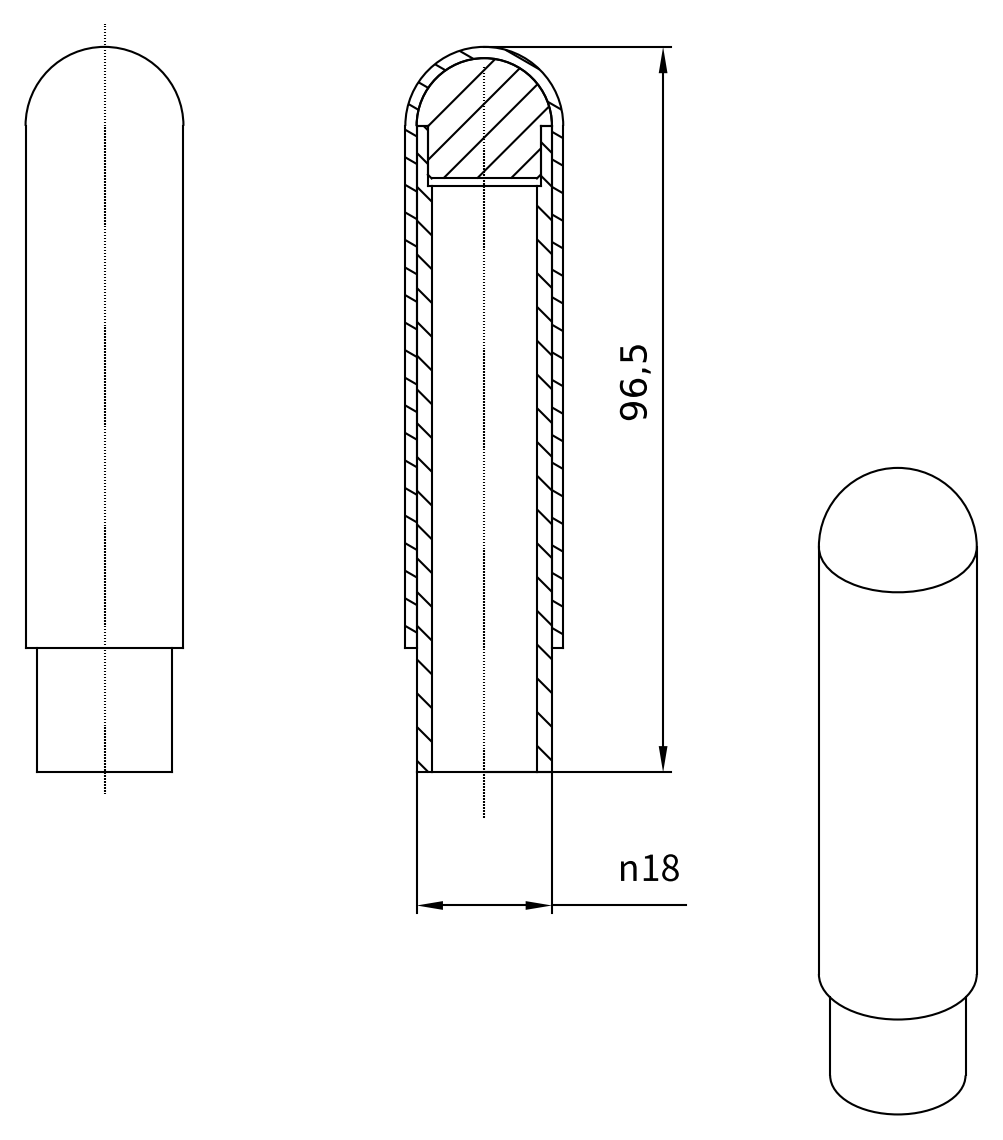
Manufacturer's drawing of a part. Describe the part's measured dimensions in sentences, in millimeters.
Its 3-D file was written by "Autodesk Inventor 8 (AUTOMOTIVE_DESIGN)". It is 1 solid with 16 faces: 4 planar, 8 cylindrical and 4 other. Overall it measures 96.5 by 21 by 21 millimeters. Its volume is 18 506 cubic millimeters and its surface area 10 114 square millimeters. Round holes: 1 of diameter 14, 1 of diameter 15. Round bosses or shafts: 1 of diameter 21, 1 of diameter 18. The main face-to-face distances are 79, 16.5, 62.5, 78, 61.5, 1.
